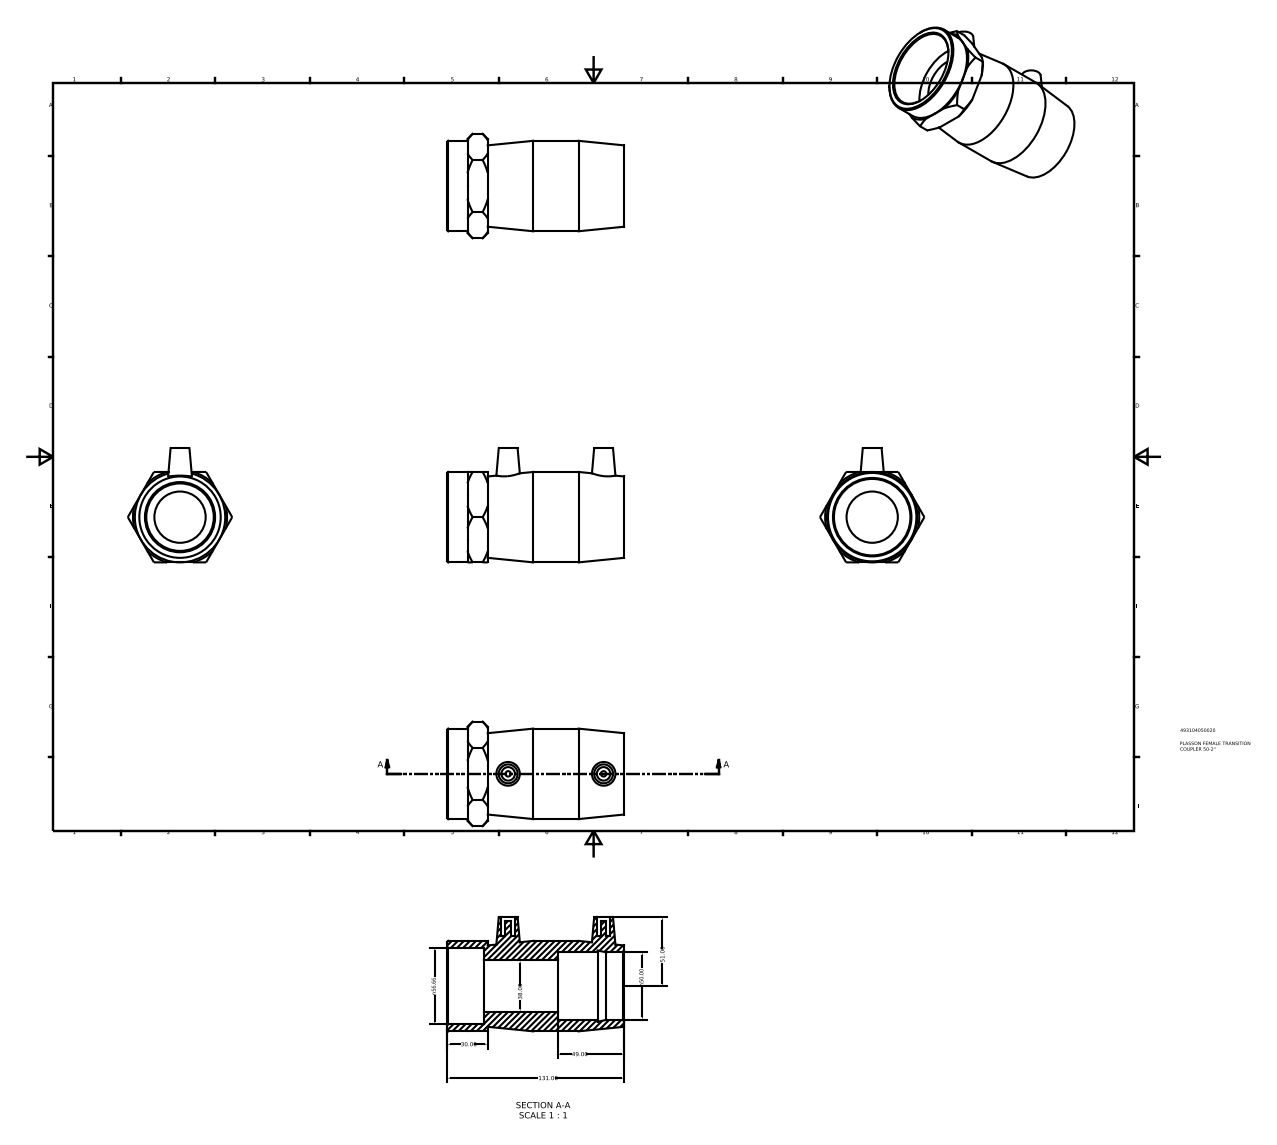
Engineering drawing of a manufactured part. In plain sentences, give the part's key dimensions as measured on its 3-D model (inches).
The part is named "493104050020". Its 3-D file was written by "Autodesk Inventor 2015 (AUTOMOTIVE_DESIGN)". It is 1 solid with 54 faces: 24 planar, 10 cylindrical and 20 other. Overall it measures 5.157 by 3.327 by 3.046 inches. Its volume is 13.55 cubic inches and its surface area 84.55 square inches. Round holes: 2 of diameter 0.394, 1 of diameter 1.496, 1 of diameter 1.969, 1 of diameter 2.231. Round bosses or shafts: 2 of diameter 0.157, 1 of diameter 2.638. The main face-to-face distances are 2.638, 0.118, 2.165, 2.047, 4.094, 3.976, 1.929, 1.063, 1.181, 3.228. The hole center spacings are 2.783.
